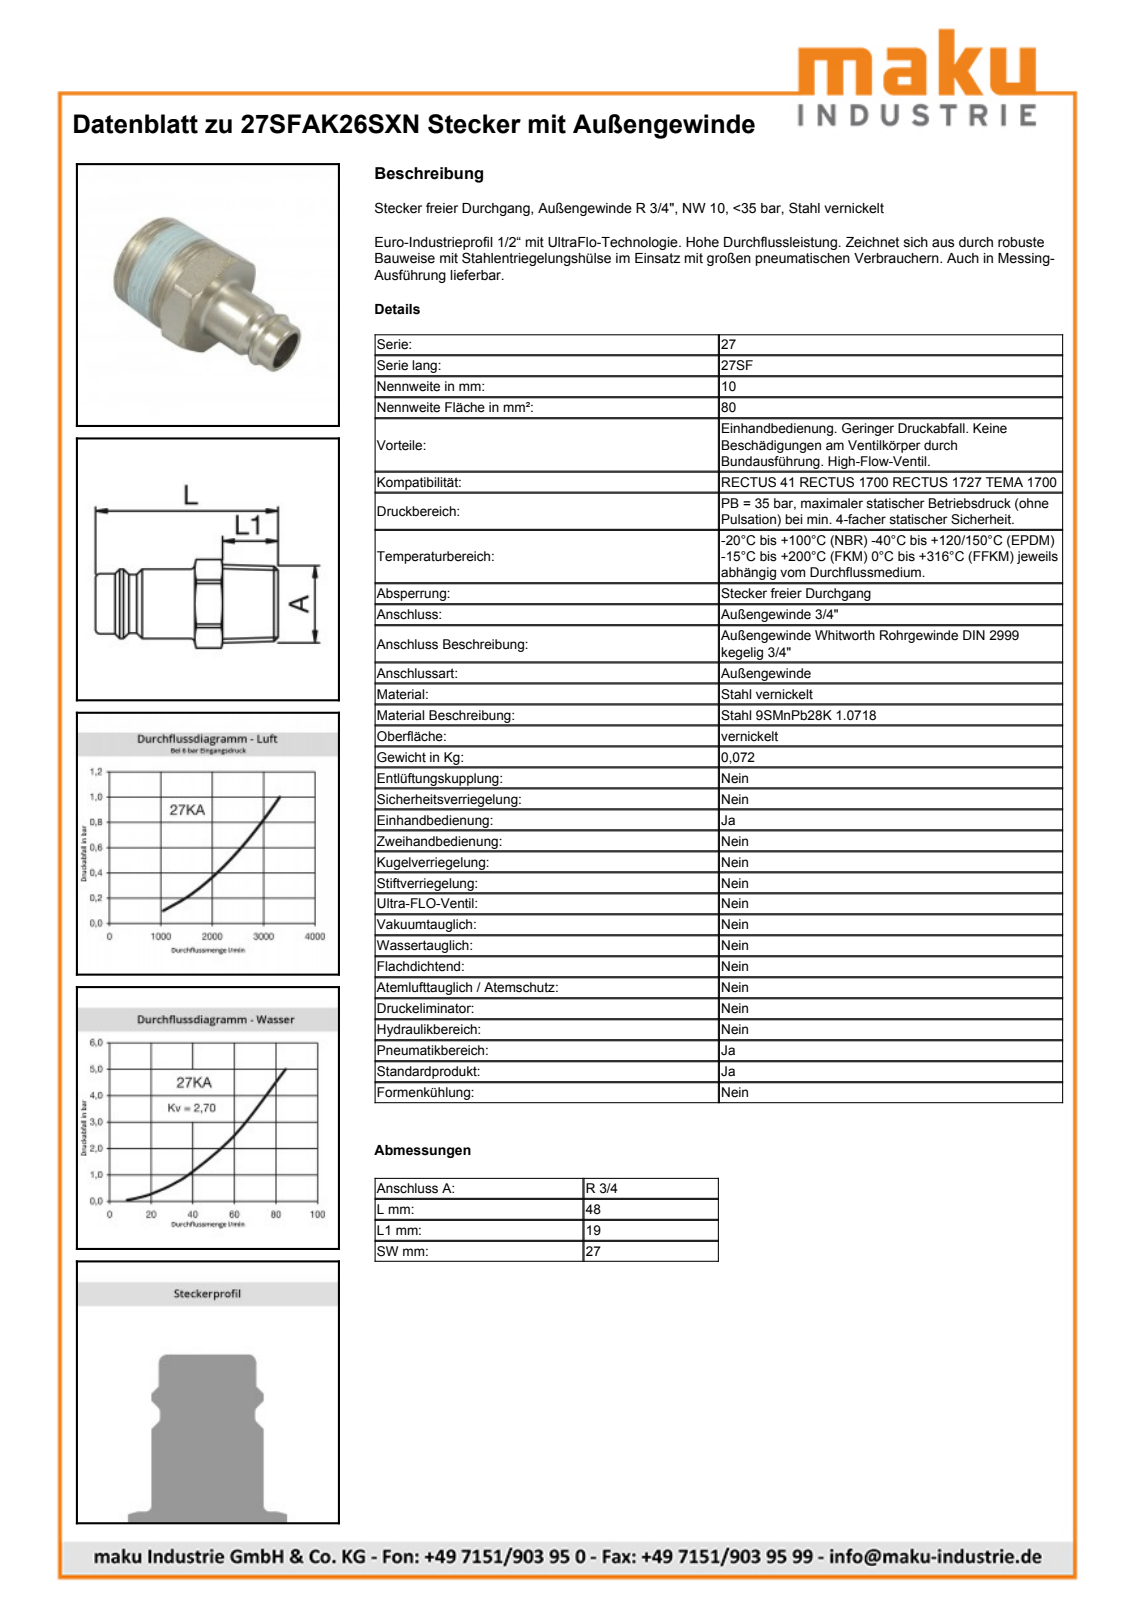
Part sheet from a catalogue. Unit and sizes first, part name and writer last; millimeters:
Units: millimetres
Overall size (bounding box): 48 × 30.45 × 27
Round holes (diameter × count): ⌀10 ×1, ⌀19 ×1
Round bosses / shafts (diameter × count): ⌀15 ×1, ⌀13 ×1, ⌀12.65 ×1
Partial cylindrical surfaces — rounded edges, fillets, slot ends (radius × count): R15.22 ×1
Main face-to-face distances: 27, 26.5, 21.5, 48
Volume: 10 191 mm³ · Surface area: 6 226 mm²
Bodies: 1 solid, 43 faces (9 planar, 12 cylindrical, 22 other)
Part name (STEP PRODUCT): D106715
STEP written by: Autodesk Inventor 2011 (AUTOMOTIVE_DESIGN)
